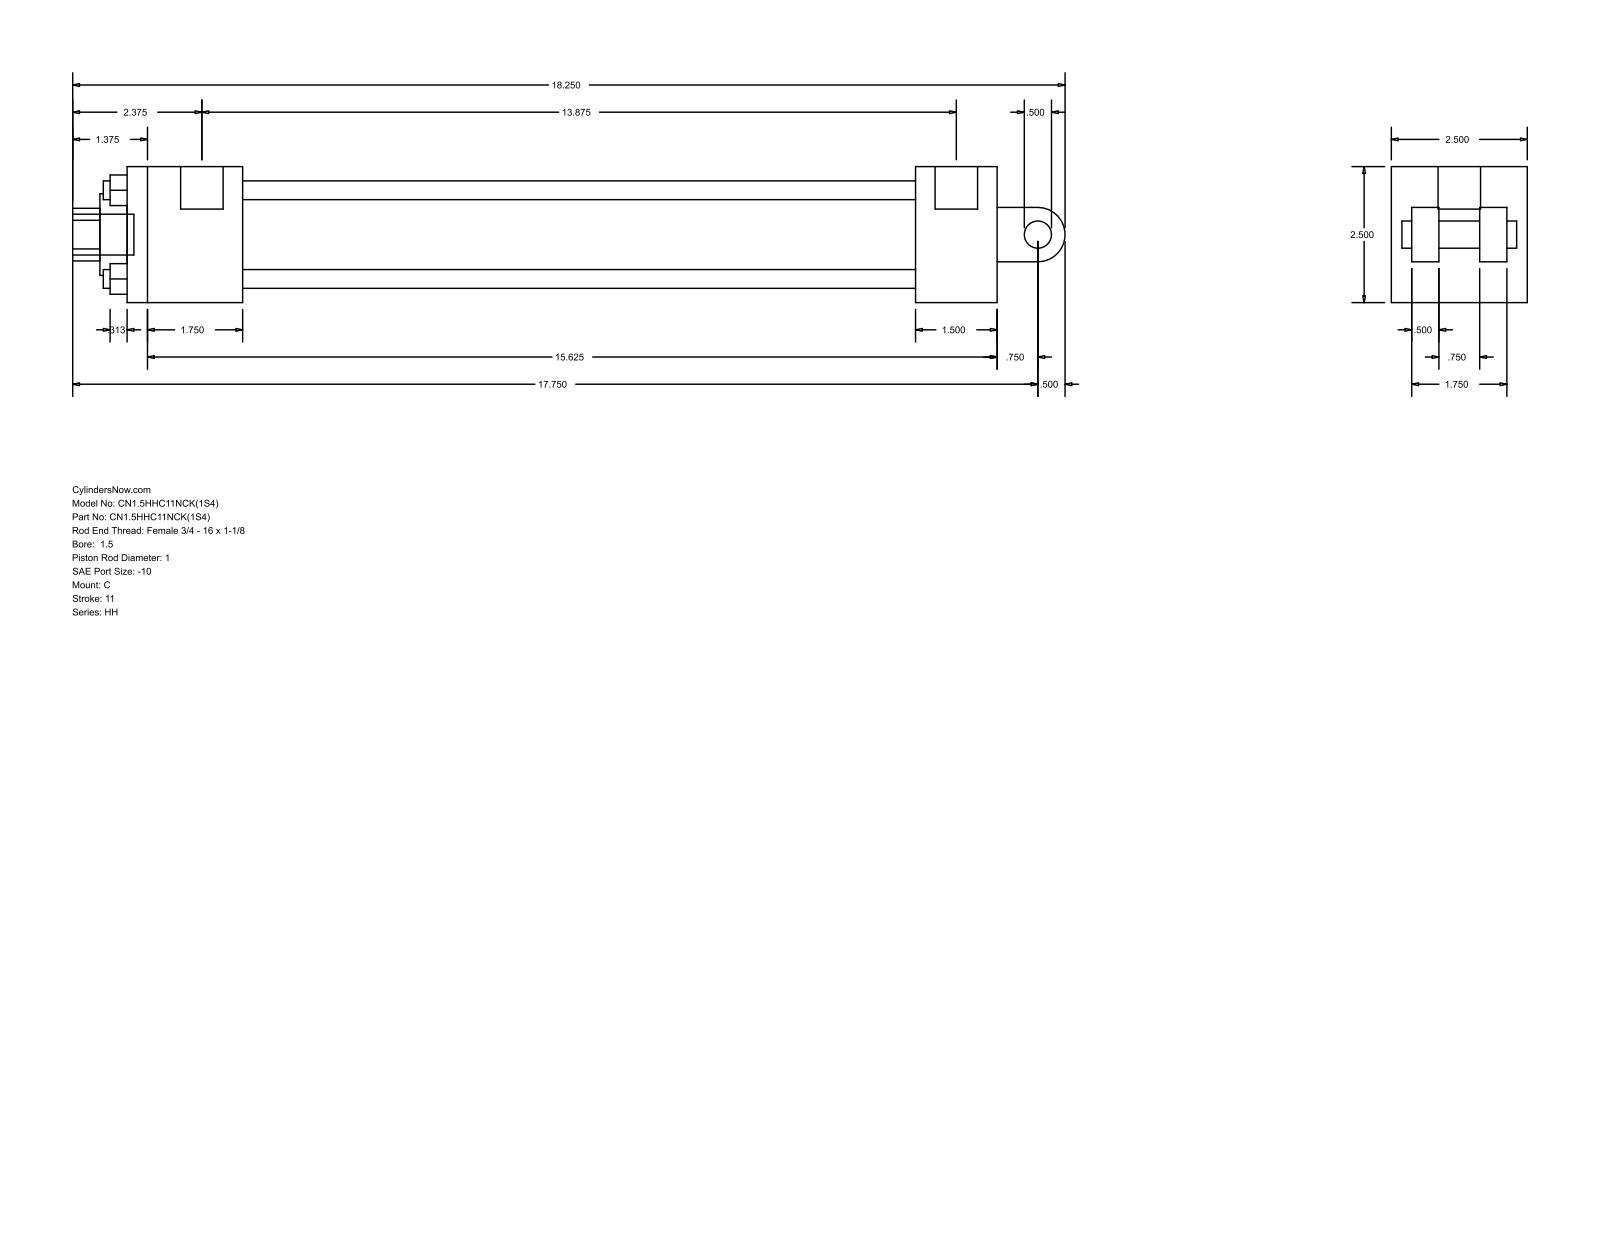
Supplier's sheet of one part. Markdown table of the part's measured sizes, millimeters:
| quantity | value |
| --- | --- |
| part name | HH_C__0150_1 |
| STEP written by | GSSL Pune (CONFIG_CONTROL_DESIGN) |
| units | millimeters |
| bodies | 0 solids, 99 faces (70 planar, 29 cylindrical, 0 other) |
| overall size | 463.55 × 63.5 × 63.5 |
| round holes (diameter × count) | 8.76 × 4, 5.56 × 2, 19.84 × 1, 25.4 × 1, 38.1 × 1, 44.45 × 1 |
| round bosses / shafts (diameter × count) | 5.56 × 2, 19.84 × 1, 19.05 × 1, 12.7 × 1 |
| partial cylindrical surfaces (radius × count) | 12.29 × 1, 12.7 × 1 |
| main face-to-face distances | 63.5, 53.98, 314.32, 352.42, 38.1, 368.3, 406.4, 12.7, 22.22, 41.28 |
| hole center spacings | 29.27, 41.4, 58.55, 1.59 |
